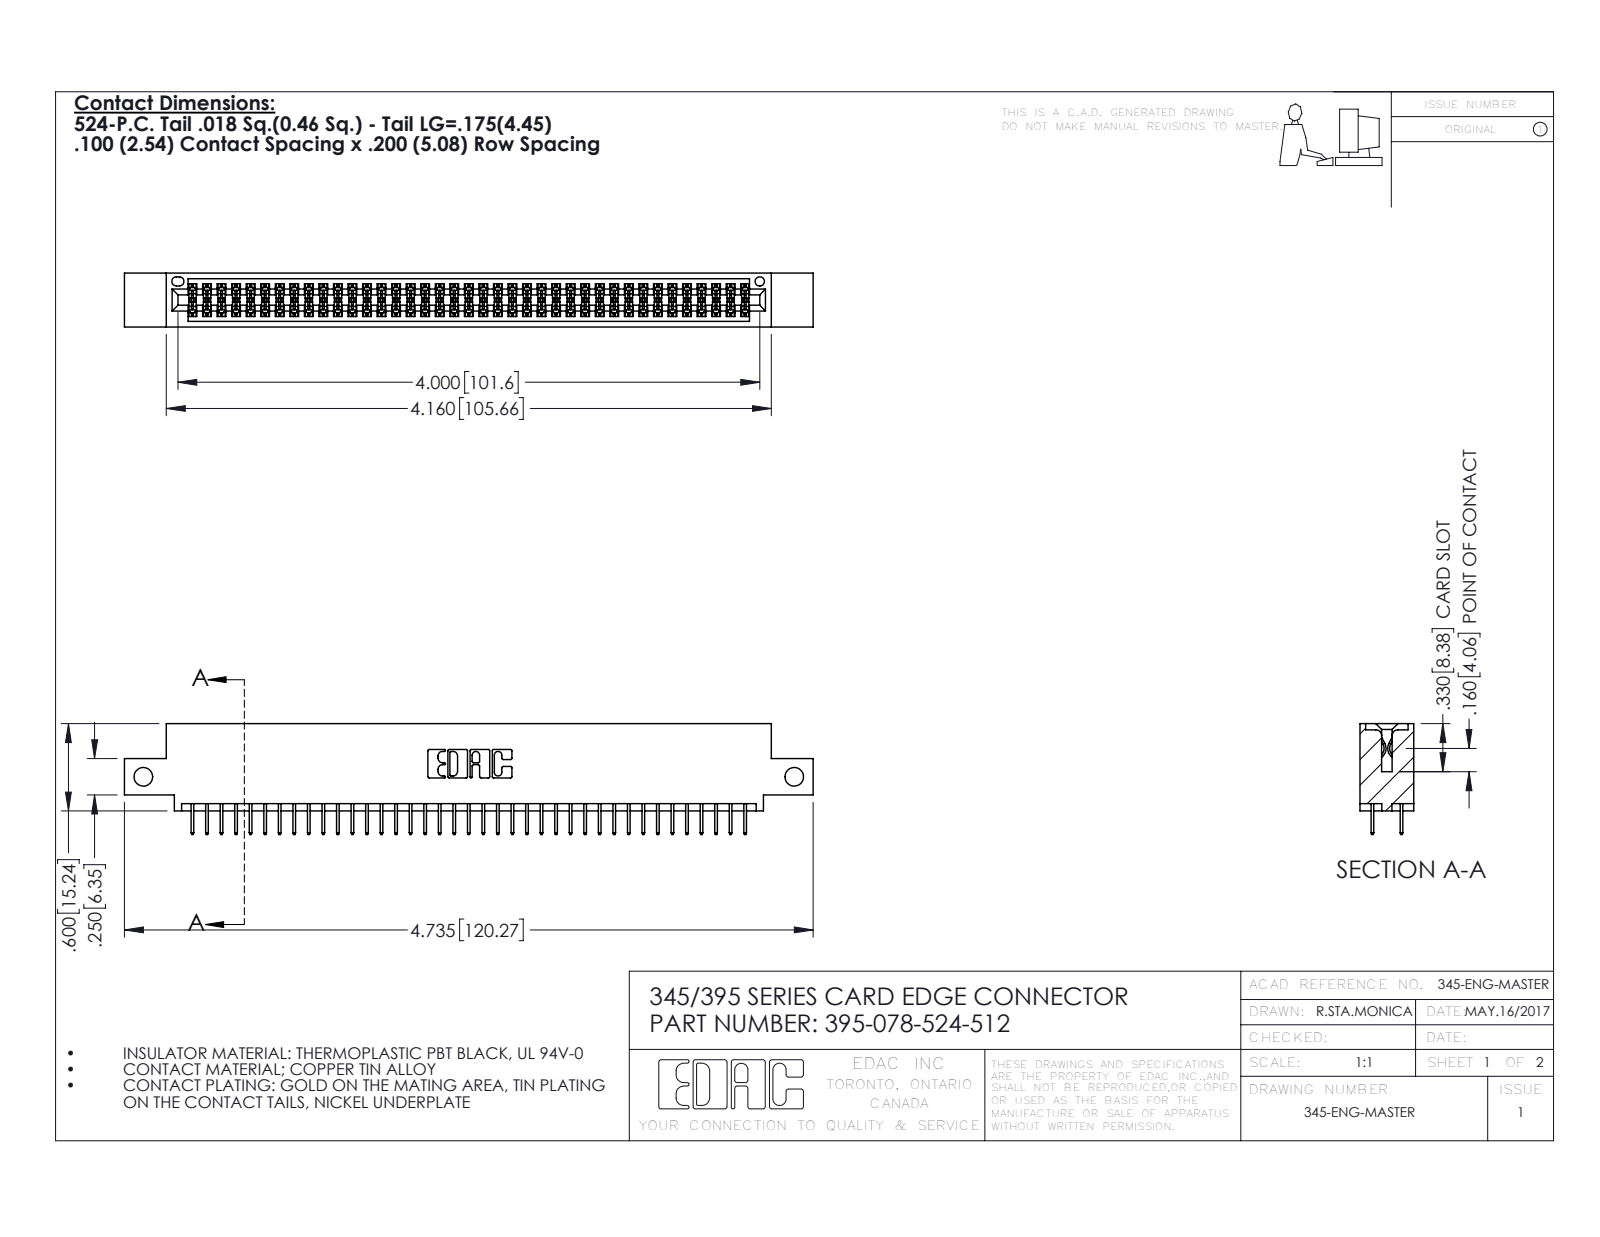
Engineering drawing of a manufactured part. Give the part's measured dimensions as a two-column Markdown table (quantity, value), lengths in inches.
| quantity | value |
| --- | --- |
| part name | 395-078-524-512; 345 Part_0.110 Offset - Side Mount; 345-292-001_345-293-124 |
| STEP written by | SolidWorks 2016 (CONFIG_CONTROL_DESIGN) |
| units | inches |
| bodies | 79 solids, 4342 faces (3126 planar, 1216 cylindrical, 0 other) |
| overall size | 4.735 × 0.762 × 0.37 |
| volume | 0.694 in³ |
| surface area | 25.43 in² |
| round holes (diameter × count) | 0.128 × 2, 0.064 × 1 |
| partial cylindrical surfaces (radius × count) | 0.006 × 117, 0.01 × 22, 0.007 × 6, 0.031 × 6, 0.026 × 3, 0.014 × 2, 0.019 × 2, 0.022 × 2 |
| main face-to-face distances | 0.072, 0.298, 0.2, 0.37, 0.098, 0.272, 0.025, 0.225, 0.072, 0.175 |
| hole center spacings | 4.475 |
